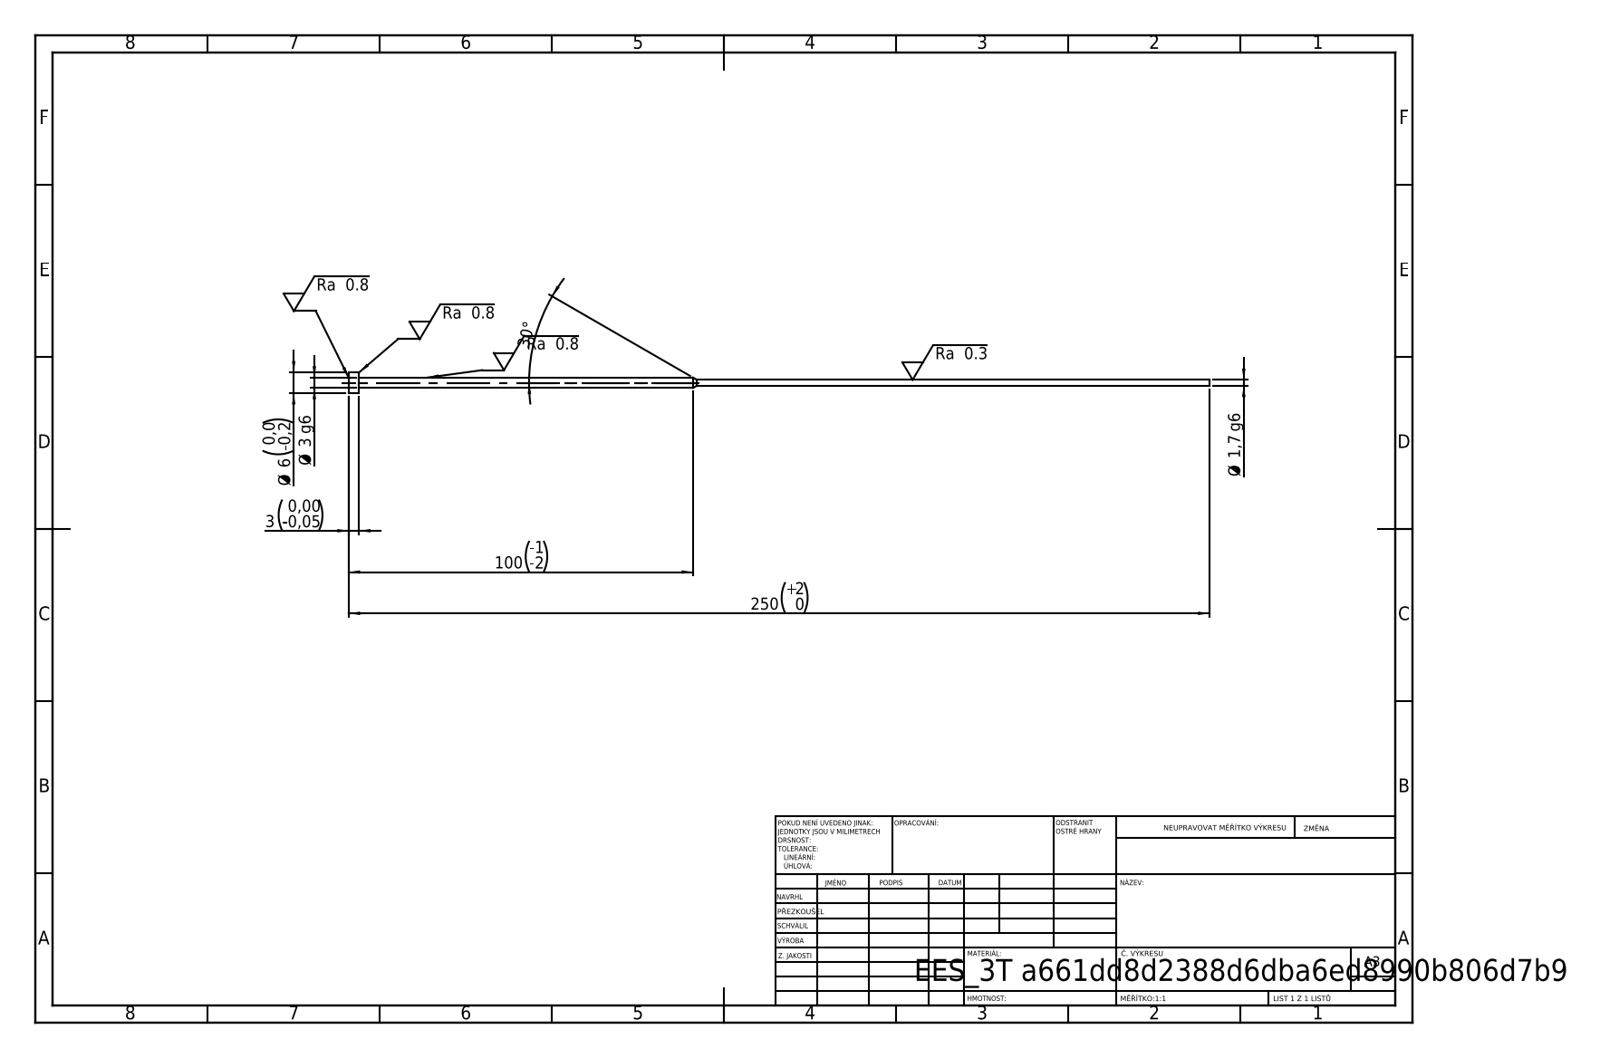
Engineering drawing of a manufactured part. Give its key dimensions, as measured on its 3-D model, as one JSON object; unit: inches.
{"step_written_by": "SolidWorks 2019 (CONFIG_CONTROL_DESIGN)", "units": "inches", "bodies": {"solids": 1, "faces": 11, "planar": 3, "cylindrical": 6, "other": 2}, "overall_size": [9.843, 0.236, 0.236], "volume_in3": 0.068, "surface_area_in2": 2.832, "round_bosses_or_shafts": [[0.236, 1], [0.118, 1], [0.067, 1]], "face_to_face_distances": [0.118, 9.724, 9.843]}
